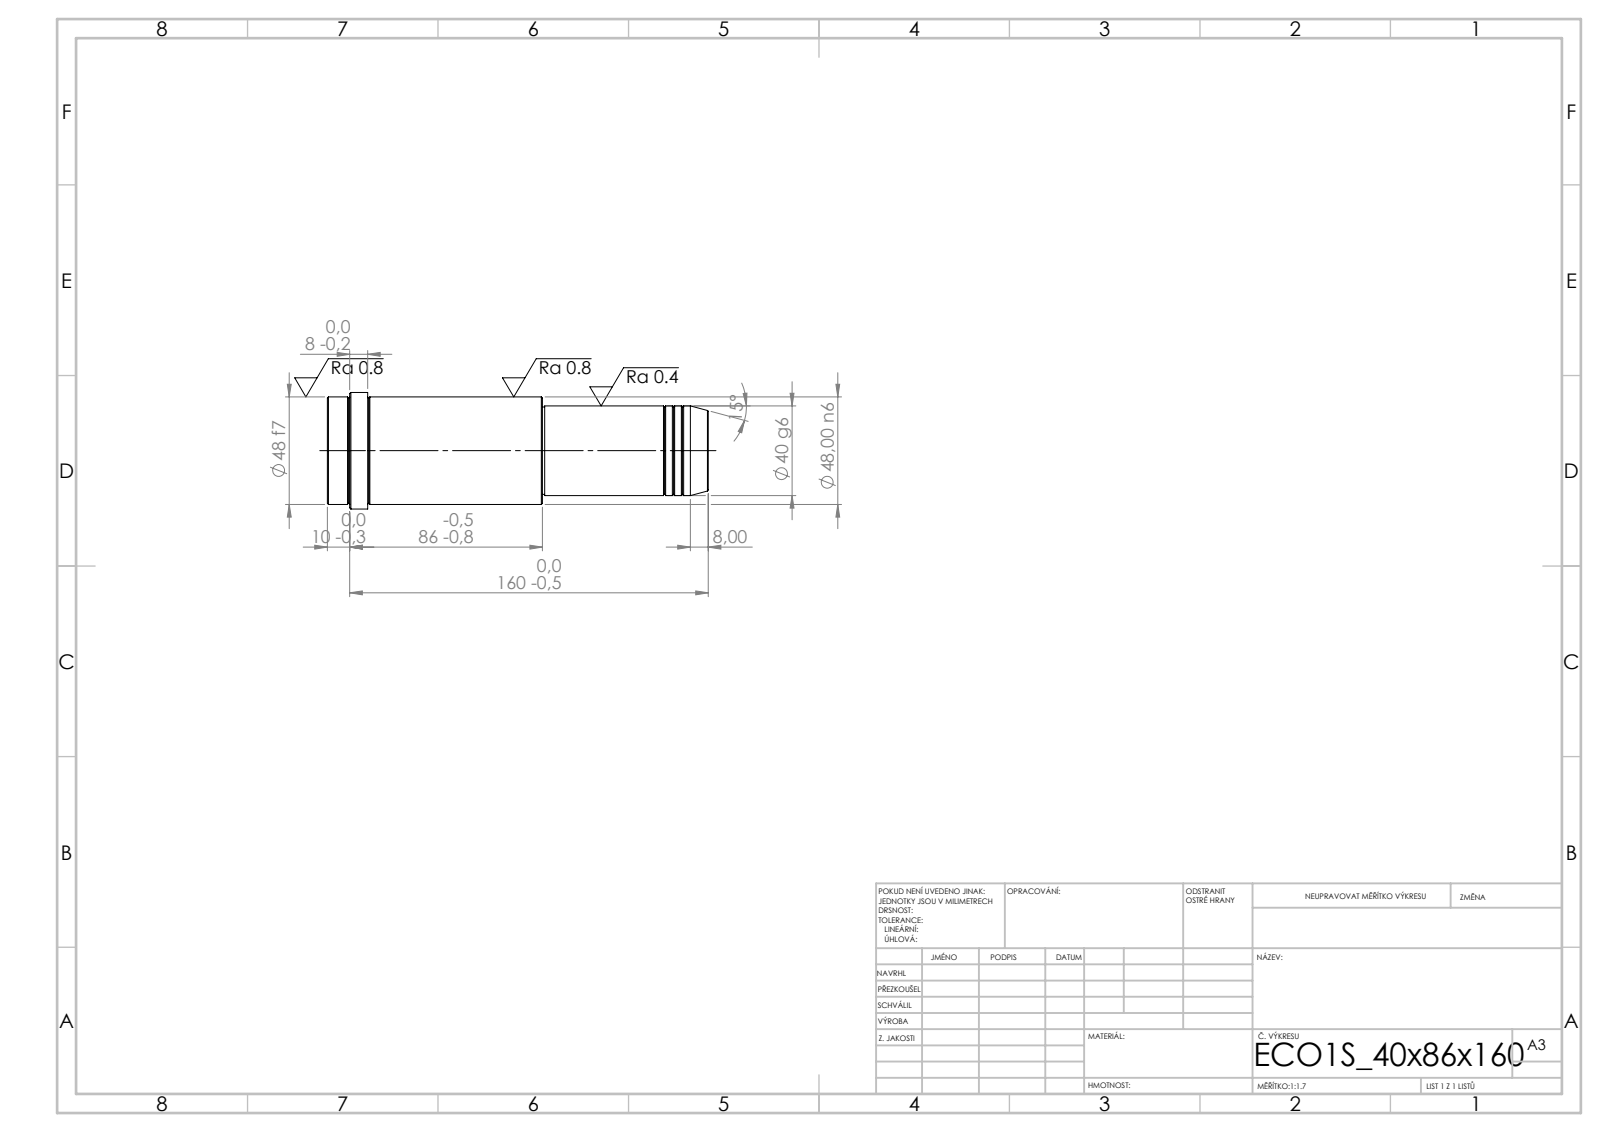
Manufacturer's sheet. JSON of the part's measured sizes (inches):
{"step_written_by": "SolidWorks 2019 (CONFIG_CONTROL_DESIGN)", "units": "inches", "bodies": {"solids": 1, "faces": 52, "planar": 6, "cylindrical": 16, "other": 30}, "overall_size": [6.693, 2.047, 2.047], "volume_in3": 16.34, "surface_area_in2": 43.7, "round_bosses_or_shafts": [[2.047, 1], [1.89, 1], [1.575, 1], [1.535, 1]], "face_to_face_distances": [6.693, 2.913, 3.78, 5.984, 3.071, 0.709, 6.299, 3.386, 0.315, 0.394]}
